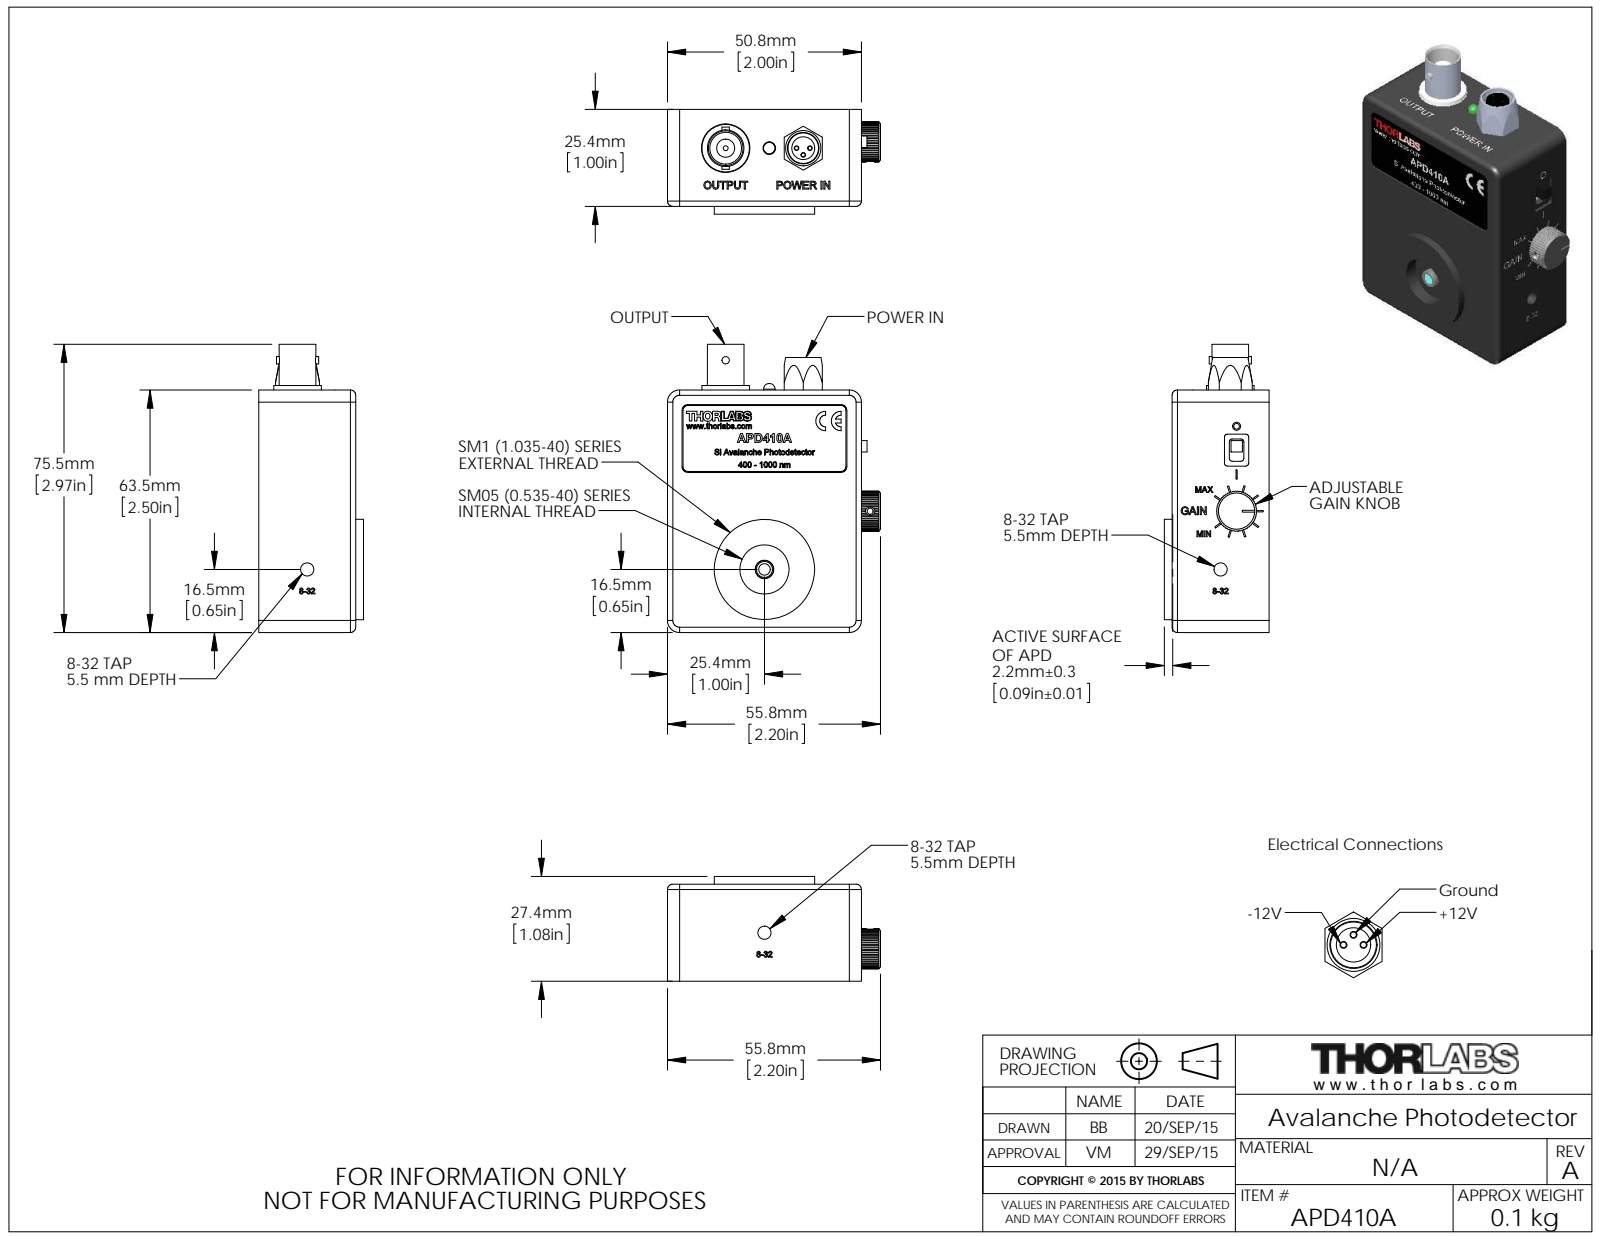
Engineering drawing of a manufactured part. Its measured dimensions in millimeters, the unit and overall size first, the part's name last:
Units: millimetres
Overall size (bounding box): 75.46 × 55.8 × 27.43
Round holes (diameter × count): ⌀1.6 ×9, ⌀0.51 ×6, ⌀2.4 ×4, ⌀0.45 ×2, ⌀2.5 ×2, ⌀3.45 ×2, ⌀1.27 ×1, ⌀1.32 ×1, ⌀2.1 ×1, ⌀3 ×1, ⌀3.3 ×1, ⌀3.5 ×1
Round bosses / shafts (diameter × count): ⌀1 ×5, ⌀3.8 ×4, ⌀2 ×4, ⌀1.64 ×2, ⌀1.6 ×2, ⌀1.3 ×2, ⌀26.29 ×1, ⌀12.45 ×1
Partial cylindrical surfaces — rounded edges, fillets, slot ends (radius × count): R0.3 ×53, R3.17 ×19, R3.3 ×14, R0.79 ×8, R2.41 ×8, R0.5 ×6, R1.91 ×6, R0.2 ×5
Main face-to-face distances: 1.59, 2.54, 0.4, 23.75, 22.16, 25.4, 23.81, 1.65, 25, 23.41
Hole centre spacings: 41.17, 4.41, 51.14, 65.51, 2.49, 43.46, 1.27, 2
Bodies: 0 solids, 2364 faces (1210 planar, 436 cylindrical, 718 other)
Part name (STEP PRODUCT): MTN005409
STEP written by: SolidWorks 2014 (AUTOMOTIVE_DESIGN)
